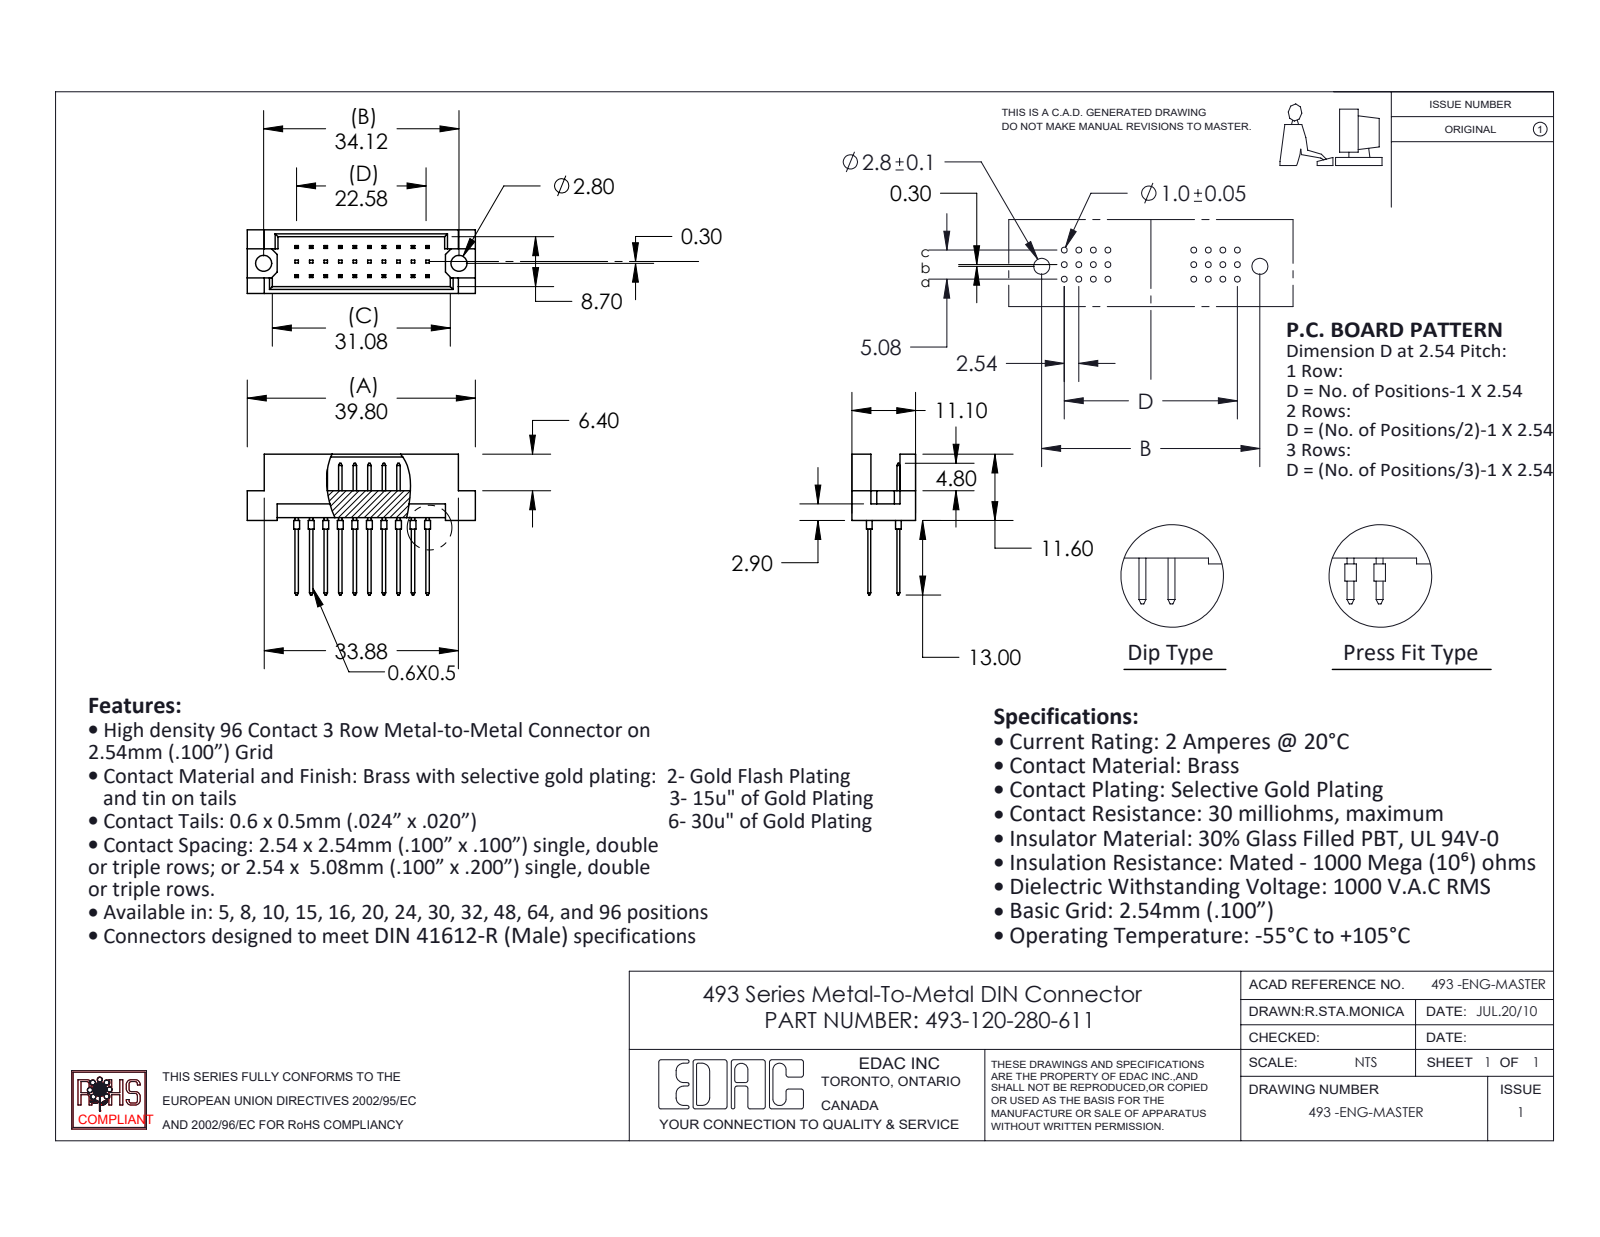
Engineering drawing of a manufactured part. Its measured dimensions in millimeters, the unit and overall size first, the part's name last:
Units: millimetres
Overall size (bounding box): 39.8 × 24.6 × 11.1
Round holes (diameter × count): ⌀2.8 ×2
Round bosses / shafts (diameter × count): ⌀1 ×20
Main face-to-face distances: 5.08, 2.54, 1.2, 9.9, 0.5, 11.1, 2.76, 3.26, 7.84, 8.34
Hole centre spacings: 34.12
Volume: 2 523 mm³ · Surface area: 3 790 mm²
Bodies: 21 solids, 612 faces (568 planar, 44 cylindrical, 0 other)
Part name (STEP PRODUCT): 493 Part_30; 493-120-280-611; 493-290_80
STEP written by: SolidWorks 2020 (CONFIG_CONTROL_DESIGN)
